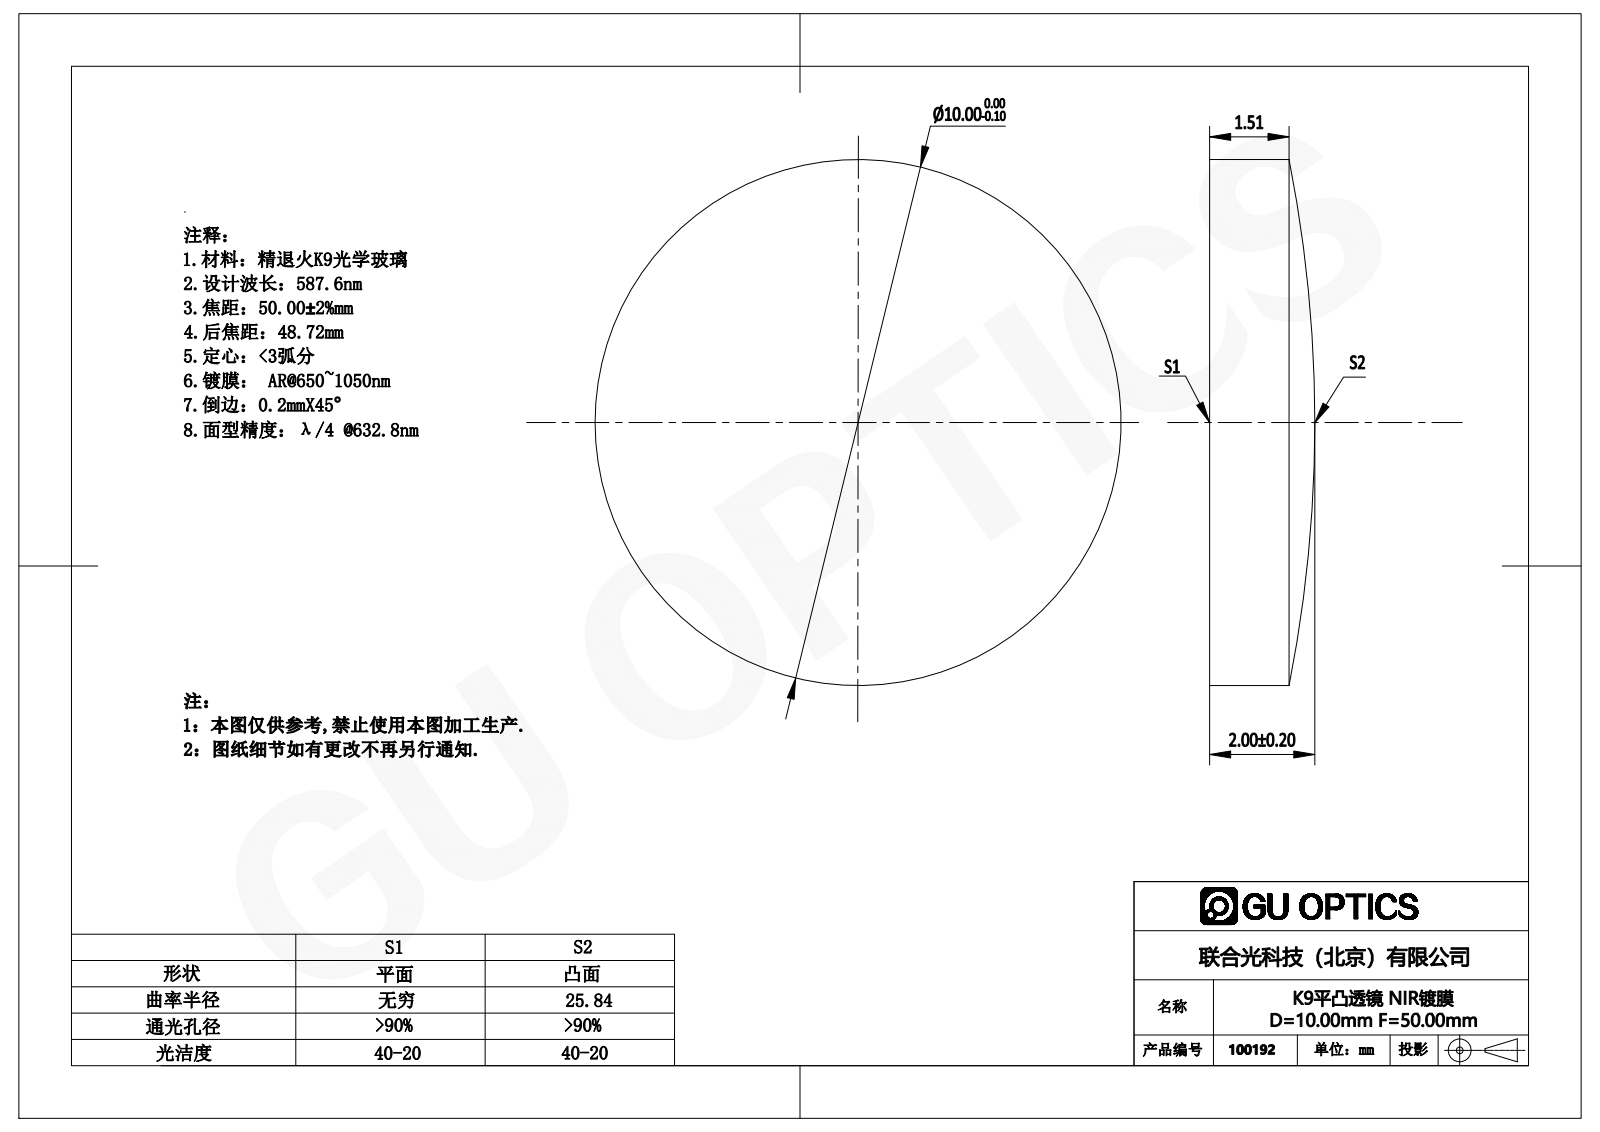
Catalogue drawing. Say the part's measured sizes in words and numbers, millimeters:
The part is named "100192". Its 3-D file was written by "SolidWorks 2016 (AUTOMOTIVE_DESIGN)". It is 1 solid with 5 faces: 1 planar, 2 cylindrical and 2 other. Overall it measures 10 by 10 by 2 millimeters. Its volume is 138 cubic millimeters and its surface area 205 square millimeters. Round bosses or shafts: 1 of diameter 10.
